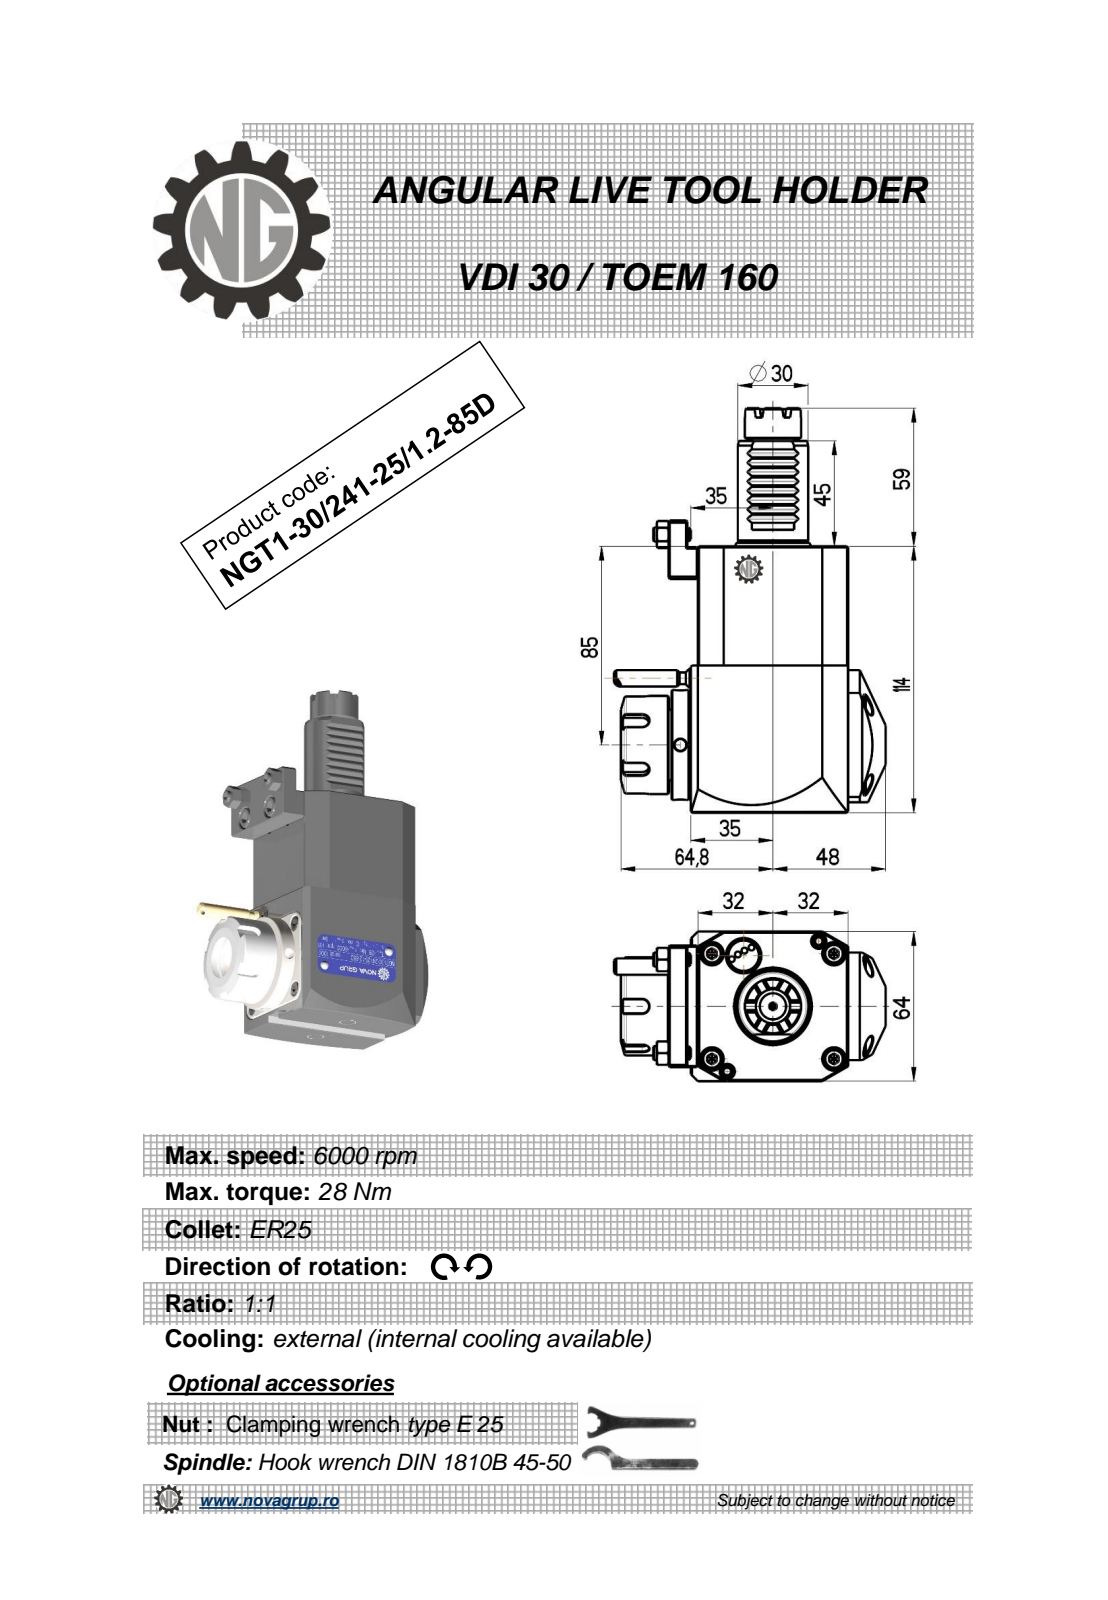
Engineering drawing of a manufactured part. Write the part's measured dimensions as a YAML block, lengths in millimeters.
part_name: "NGT1_30_241_25_1_2_85D"
step_written_by: "PRO/ENGINEER BY PARAMETRIC TECHNOLOGY CORPORATION, 2010280 (CONFIG_CONTROL_DESIGN)"
units: millimeters
bodies: {solids: 1, faces: 444, planar: 196, cylindrical: 80, other: 168}
overall_size: [173, 115.83, 64]
volume: 583753
surface_area: 56114
round_holes:
  - {diameter: 5, count: 2}
  - {diameter: 2.5, count: 1}
  - {diameter: 3, count: 1}
  - {diameter: 20.3, count: 1}
round_bosses_or_shafts:
  - {diameter: 6, count: 2}
  - {diameter: 47, count: 1}
  - {diameter: 42, count: 1}
  - {diameter: 35, count: 1}
  - {diameter: 30, count: 1}
  - {diameter: 24, count: 1}
  - {diameter: 17.7, count: 1}
  - {diameter: 15.2, count: 1}
partial_cylinders:
  - {radius: 0.31, count: 10}
  - {radius: 0.3, count: 8}
  - {radius: 3, count: 5}
  - {radius: 3.5, count: 2}
  - {radius: 160, count: 2}
  - {radius: 32, count: 1}
face_to_face_distances: [64, 114, 3, 9.3, 0.5, 8, 3.2, 67.2, 1.3, 67]
hole_center_spacings: [33.19]
